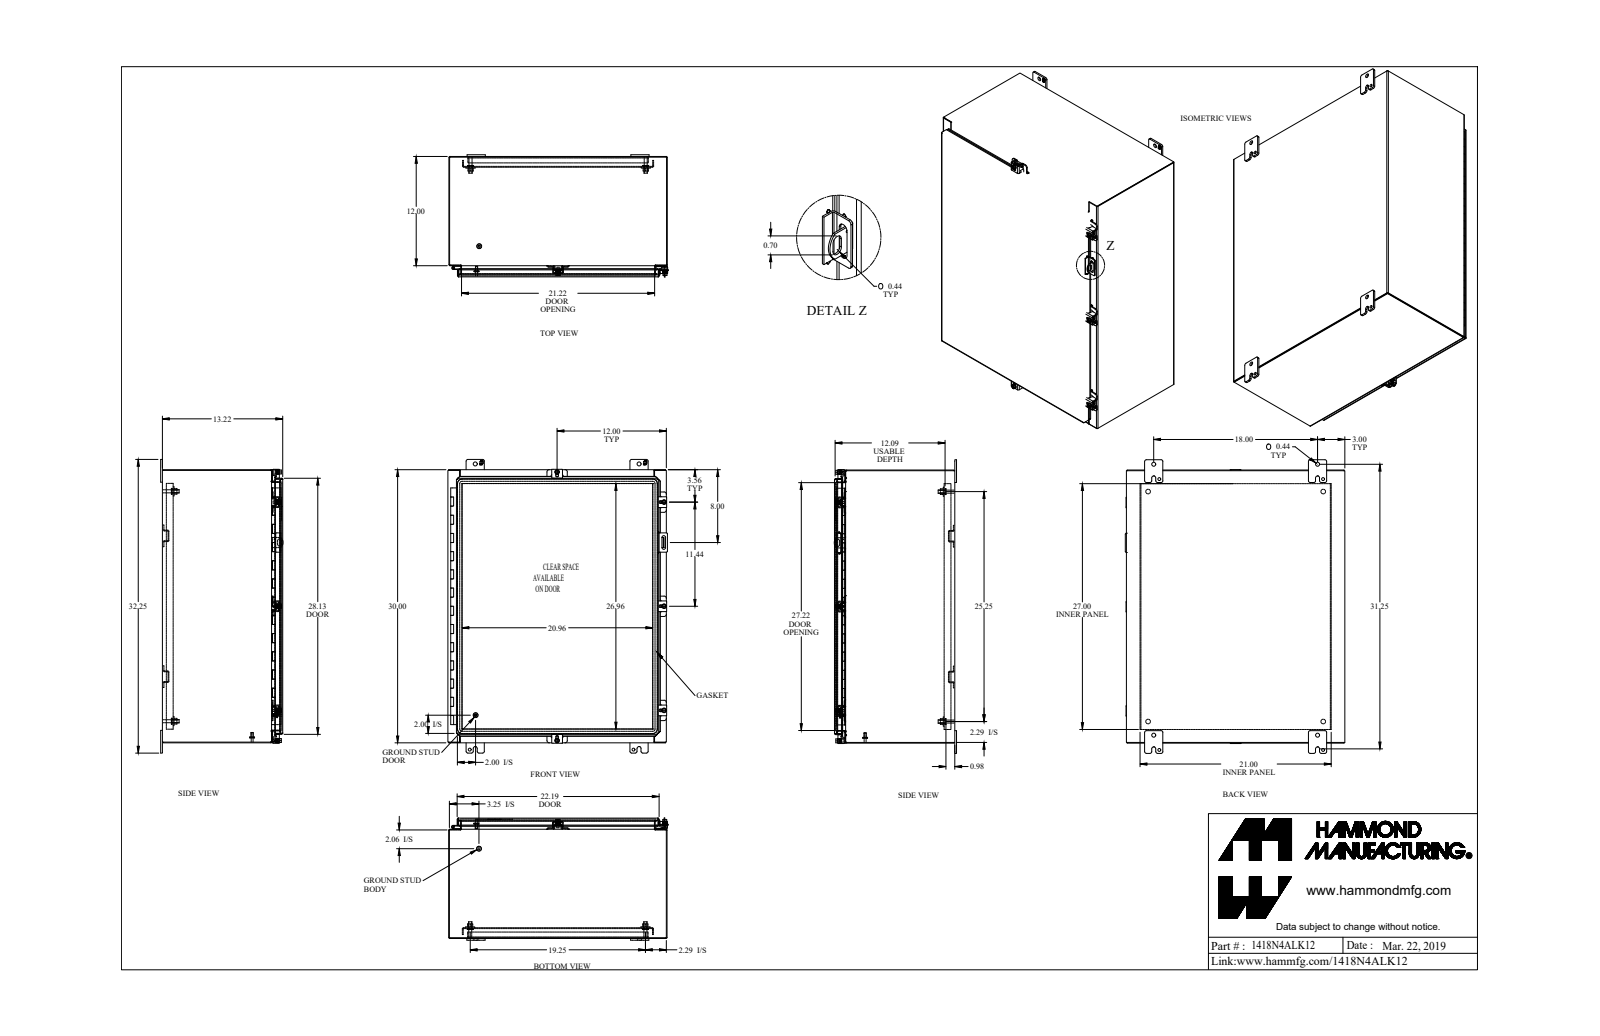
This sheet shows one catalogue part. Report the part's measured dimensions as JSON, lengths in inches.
{"part_name": "1418N4ALK12_Default", "step_written_by": "SolidWorks 2019 (CONFIG_CONTROL_DESIGN)", "units": "inches", "bodies": {"solids": 46, "faces": 1723, "planar": 1049, "cylindrical": 608, "other": 66}, "overall_size": [32.25, 24.126, 13.438], "volume_in3": 339.9, "surface_area_in2": 7891, "round_holes": [[0.232, 5], [0.265, 5], [0.375, 5], [0.313, 4], [0.437, 4], [0.5, 4], [0.307, 2], [0.445, 2], [0.125, 1], [0.187, 1]], "round_bosses_or_shafts": [[0.131, 14], [0.5, 5], [0.4, 5], [0.244, 5], [0.65, 4], [0.375, 4], [0.33, 4], [1, 2]], "partial_cylinders_radius": [[0.05, 26], [0.15, 26], [0.188, 24], [0.25, 24], [0.041, 14], [0.122, 14], [0.04, 10], [0.121, 10]], "face_to_face_distances": [0.081, 23.919, 0.1, 13.041, 13.122, 13.141, 13.222, 0.095, 29.919, 12.046], "hole_center_spacings": [29.018, 1.736, 18, 29.75, 31.751, 34.772, 9.857, 9.857]}
